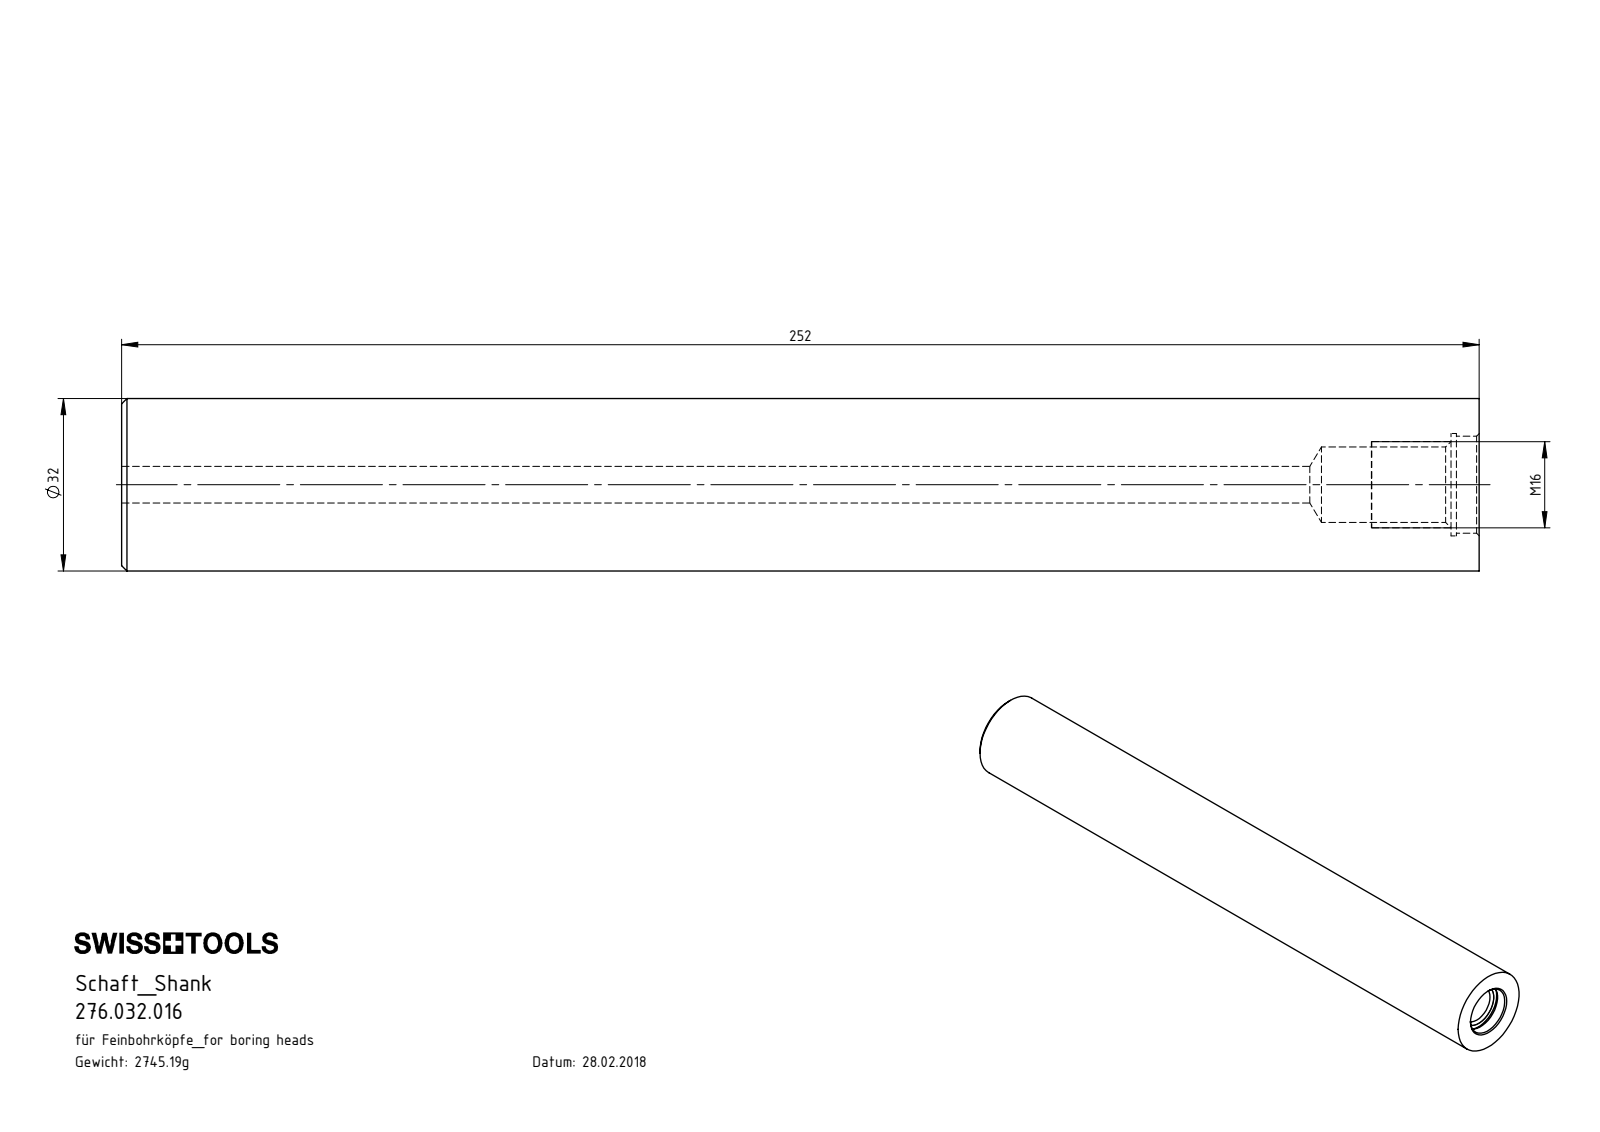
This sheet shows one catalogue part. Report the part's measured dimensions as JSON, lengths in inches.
{"part_name": "276.032.016", "step_written_by": "SolidWorks 2017 (CONFIG_CONTROL_DESIGN)", "units": "inches", "bodies": {"solids": 1, "faces": 22, "planar": 4, "cylindrical": 10, "other": 8}, "overall_size": [9.921, 1.26, 1.26], "volume_in3": 11.55, "surface_area_in2": 51.02, "round_holes": [[0.268, 1], [0.551, 1], [0.709, 1], [0.748, 1]], "round_bosses_or_shafts": [[1.26, 1]], "face_to_face_distances": [9.921, 9.715, 0.207, 9.754, 0.039, 0.167]}
